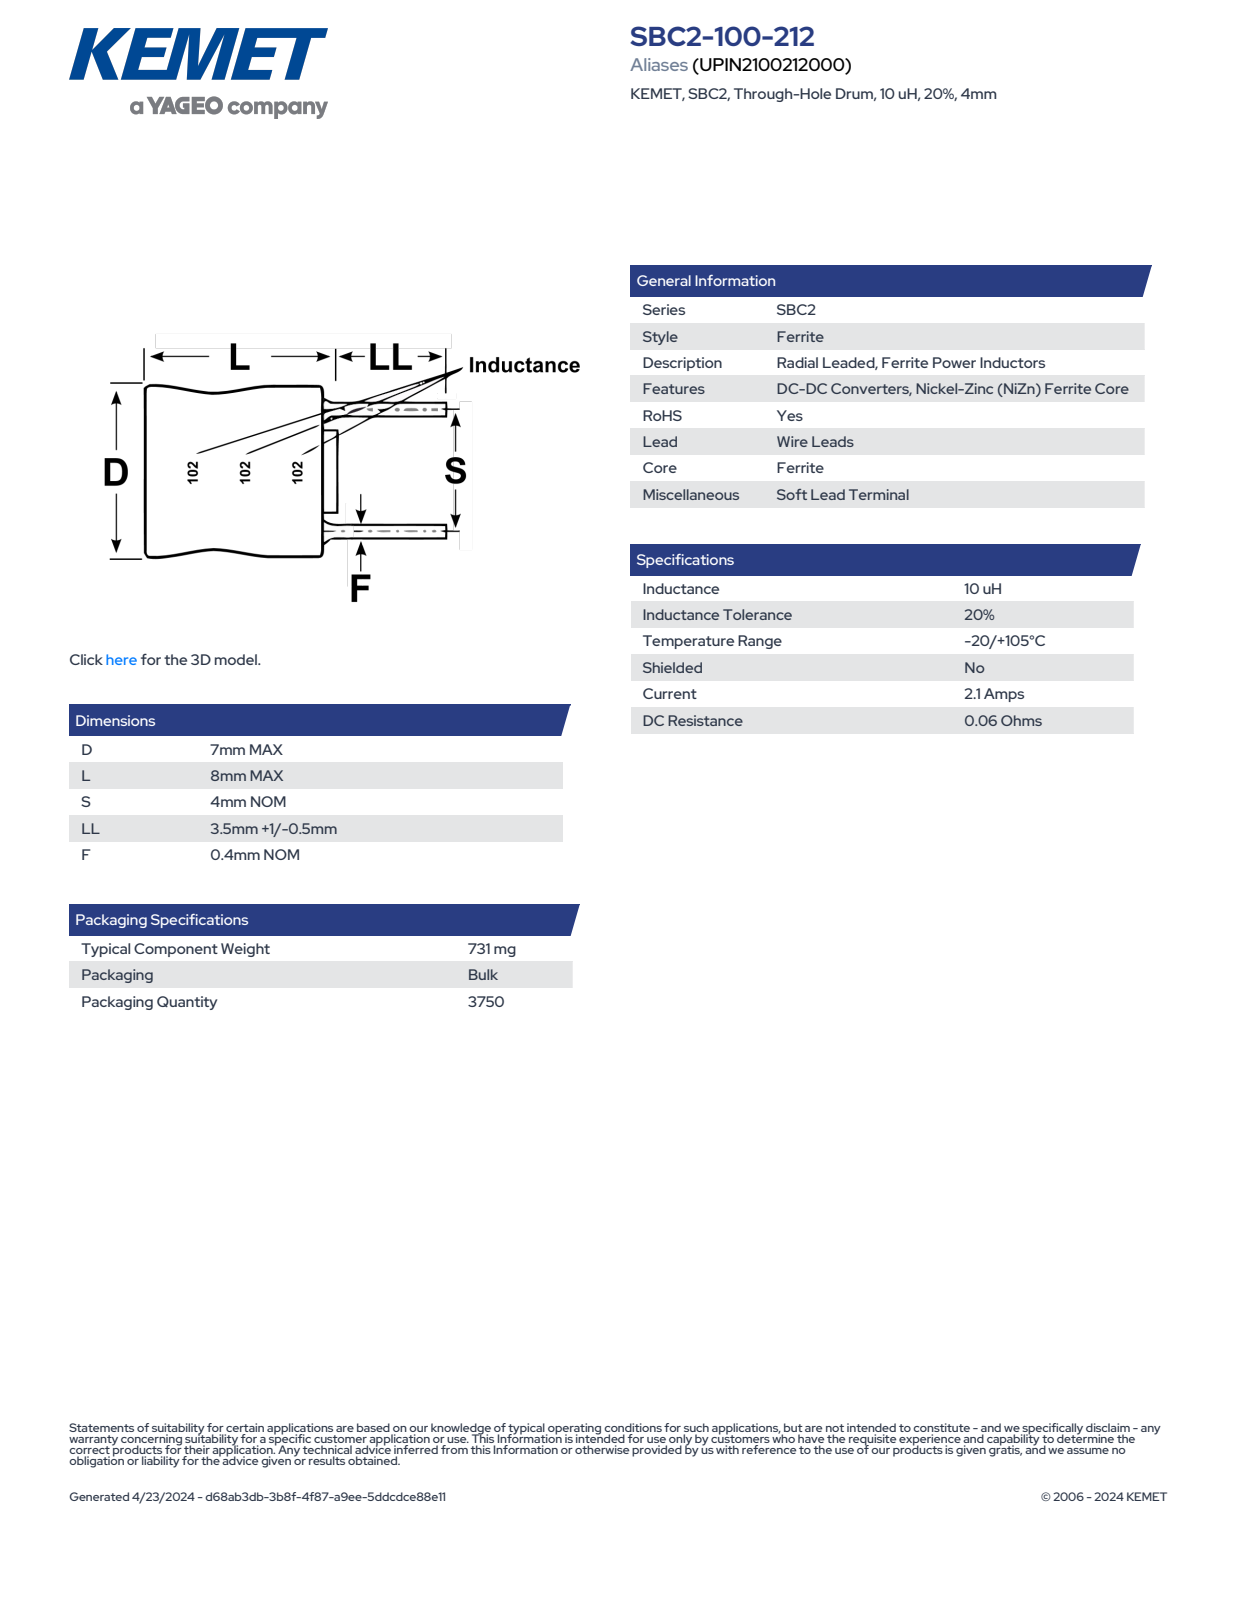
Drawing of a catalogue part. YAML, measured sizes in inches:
part_name: "IL_SBCP_D7L8S4LL4.5F0.4"
step_written_by: "SolidWorks 2014 (AUTOMOTIVE_DESIGN)"
units: inches
bodies: {solids: 4, faces: 84, planar: 66, cylindrical: 10, other: 8}
overall_size: [0.493, 0.276, 0.276]
volume: 0.016
surface_area: 0.395
round_bosses_or_shafts:
  - {diameter: 0.016, count: 2}
  - {diameter: 0.276, count: 1}
  - {diameter: 0.251, count: 1}
face_to_face_distances: [0.306, 0.306, 0.315, 0.315, 0.177, 0.187, 0.492, 0.493, 0.105, 0.015]
